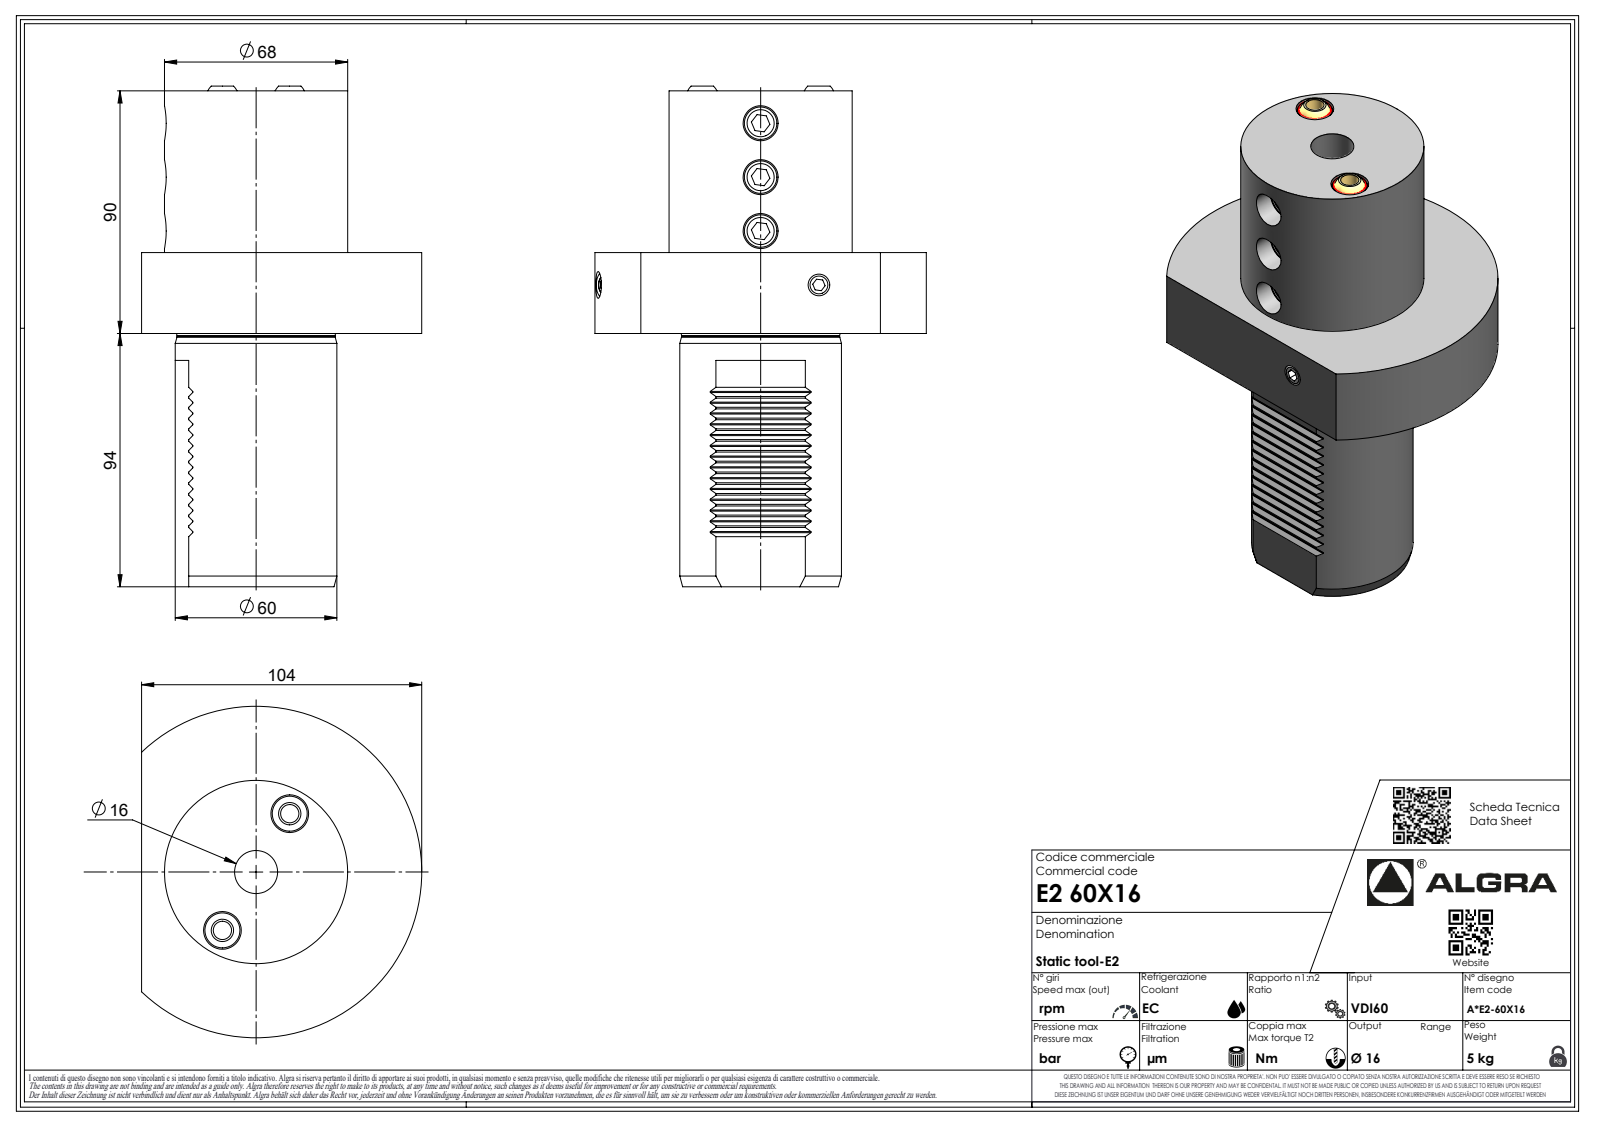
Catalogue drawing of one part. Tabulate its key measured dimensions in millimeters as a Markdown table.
| quantity | value |
| --- | --- |
| part name | E260X16 |
| STEP written by | SolidWorks 2023 (AUTOMOTIVE_DESIGN) |
| units | millimeters |
| bodies | 1 solid, 282 faces (192 planar, 45 cylindrical, 45 other) |
| overall size | 185.77 × 123 × 104 |
| volume | 780 115 mm³ |
| surface area | 67 234 mm² |
| round holes (diameter × count) | 2.1 × 1, 16 × 1 |
| round bosses / shafts (diameter × count) | 68 × 1, 60 × 1, 58.7 × 1, 6.37 × 1, 1.7 × 1 |
| partial cylindrical surfaces (radius × count) | 0.3 × 14, 0.33 × 7, 0.52 × 7, 3.7 × 7, 0.21 × 1, 61.5 × 1 |
| main face-to-face distances | 30, 90, 60, 94, 124, 184, 2.83, 14.14, 11.31, 17.5 |
